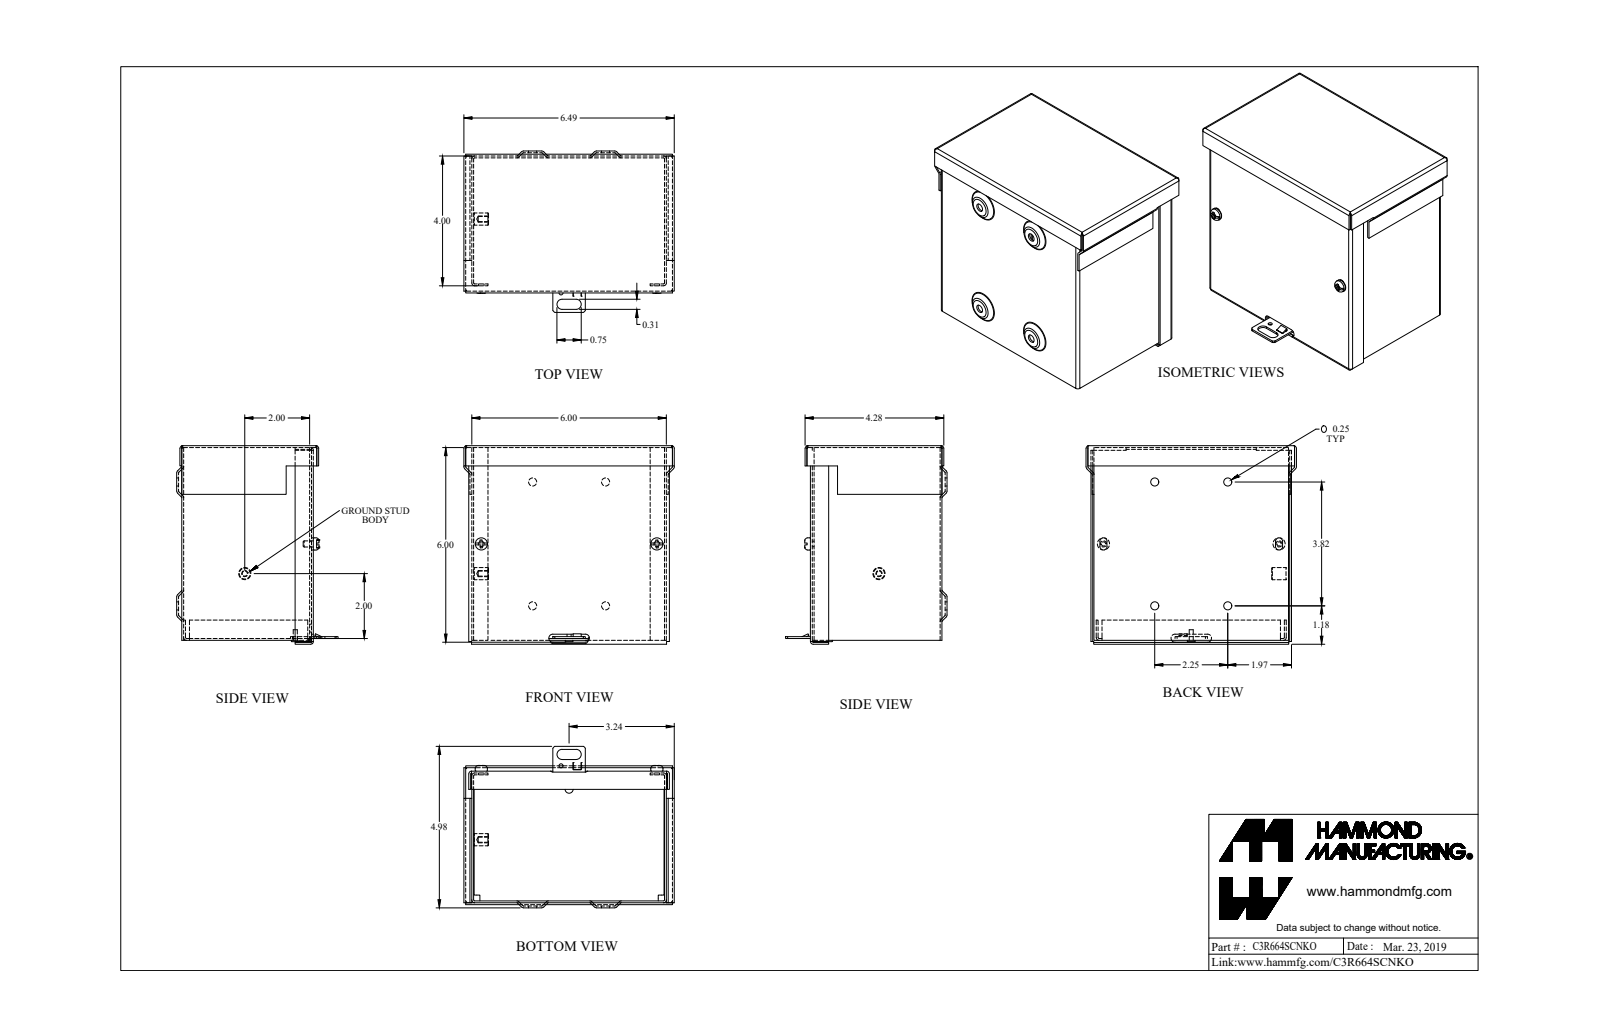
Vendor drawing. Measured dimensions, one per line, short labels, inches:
name: C3R664SCNKO_Default
written by: SolidWorks 2019 (CONFIG_CONTROL_DESIGN)
unit: in
bodies: 9 solids, 338 faces (173 planar, 91 cylindrical, 74 other)
size: 6.489 × 6.12 × 4.977
volume: 12.22 in³; area: 436.1 in²
holes: 4× ⌀0.25, 2× ⌀0.17, 1× ⌀0.125, 1× ⌀0.137, 1× ⌀0.156
bosses: 3× ⌀0.375, 2× ⌀0.19, 1× ⌀0.125
rounds: 21× R0.029, 21× R0.086, 8× R0.125, 4× R0.109, 2× R0.156
face distances: 0.057, 4, 5.943, 6, 3.943, 0.057, 4.057, 5.886, 5.886, 5.943
hole spacings: 2.48, 4.281, 2.25, 3.818, 4.431, 0.763, 5.414
